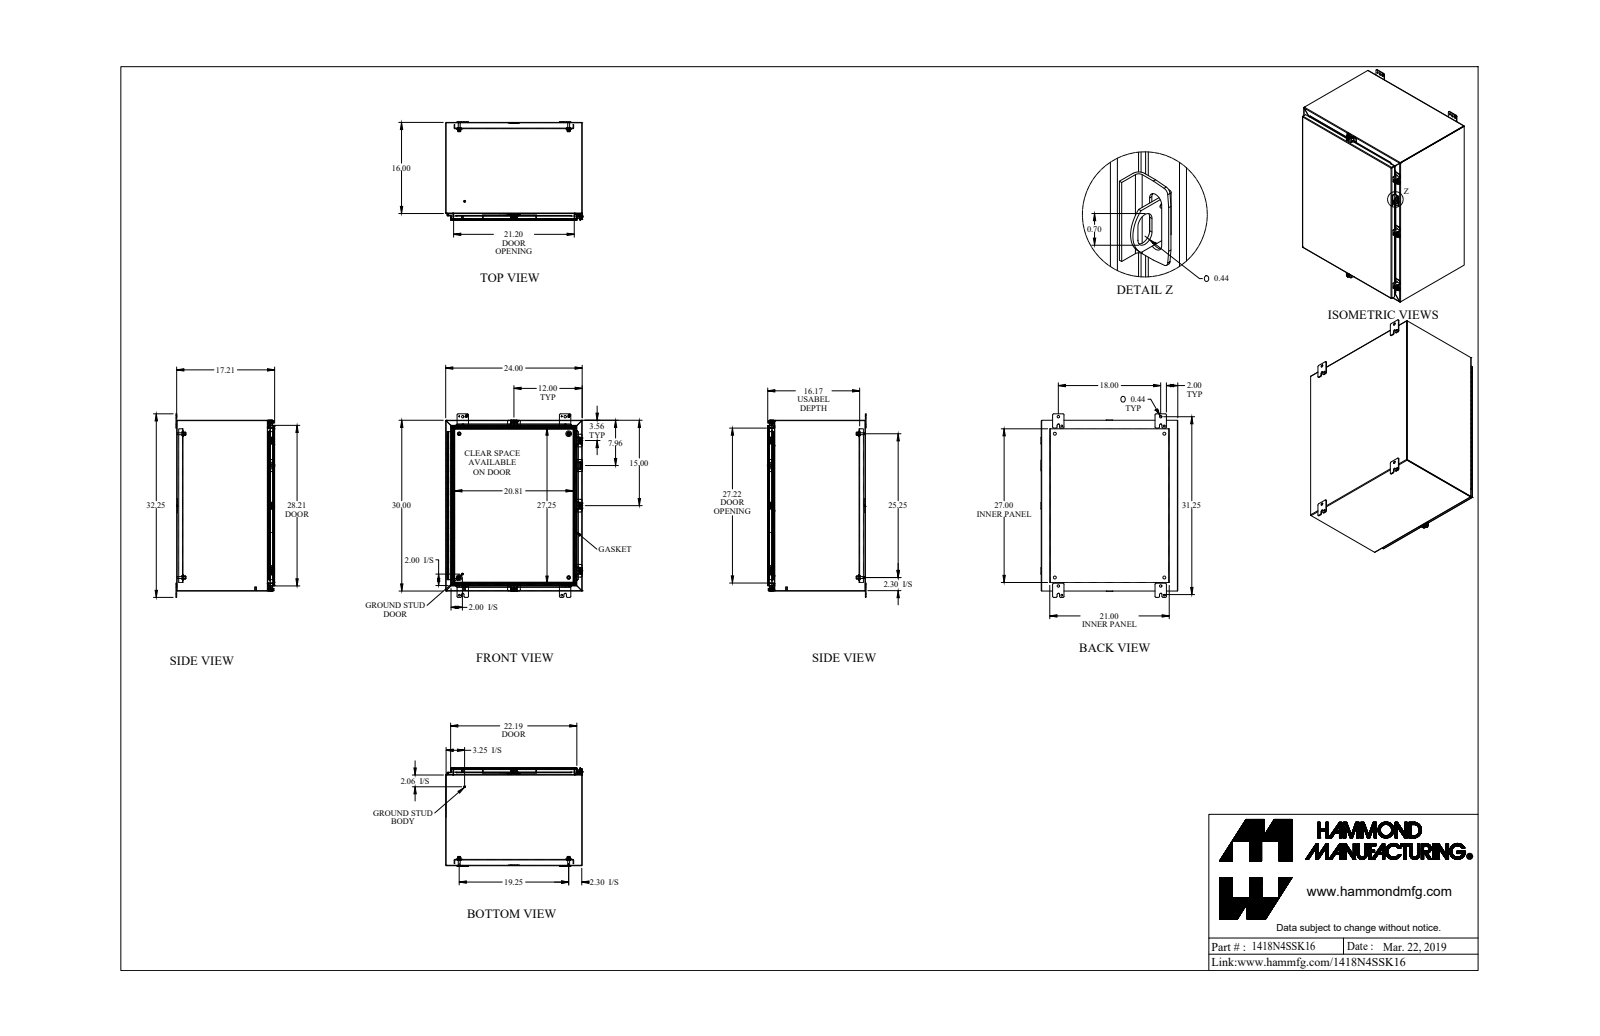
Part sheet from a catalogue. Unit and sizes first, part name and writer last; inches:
Units: inches
Overall size (bounding box): 32.25 × 24.063 × 17.375
Round holes (diameter × count): ⌀0.213 ×5, ⌀0.265 ×5, ⌀0.375 ×5, ⌀0.313 ×4, ⌀0.437 ×4, ⌀0.5 ×4, ⌀0.307 ×2, ⌀0.445 ×2, ⌀0.125 ×1, ⌀0.187 ×1
Round bosses / shafts (diameter × count): ⌀0.5 ×5, ⌀0.39 ×5, ⌀0.244 ×5, ⌀0.65 ×4, ⌀0.375 ×4, ⌀0.332 ×4, ⌀1 ×2, ⌀0.313 ×2
Partial cylindrical surfaces — rounded edges, fillets, slot ends (radius × count): R0.048 ×27, R0.143 ×27, R0.188 ×26, R0.25 ×24, R0.036 ×22, R0.108 ×22, R0.125 ×10, R0.141 ×10
Main face-to-face distances: 0.072, 23.928, 29.928, 0.072, 17.066, 17.138, 17.138, 17.21, 0.095, 0.937
Hole centre spacings: 29.018, 1.736, 9.857, 18, 25.25, 29.75, 31.751, 34.772
Volume: 320 in³ · Surface area: 8 501 in²
Bodies: 45 solids, 1653 faces (1021 planar, 546 cylindrical, 86 other)
Part name (STEP PRODUCT): 1418N4SSK16_Default
STEP written by: SolidWorks 2019 (CONFIG_CONTROL_DESIGN)
